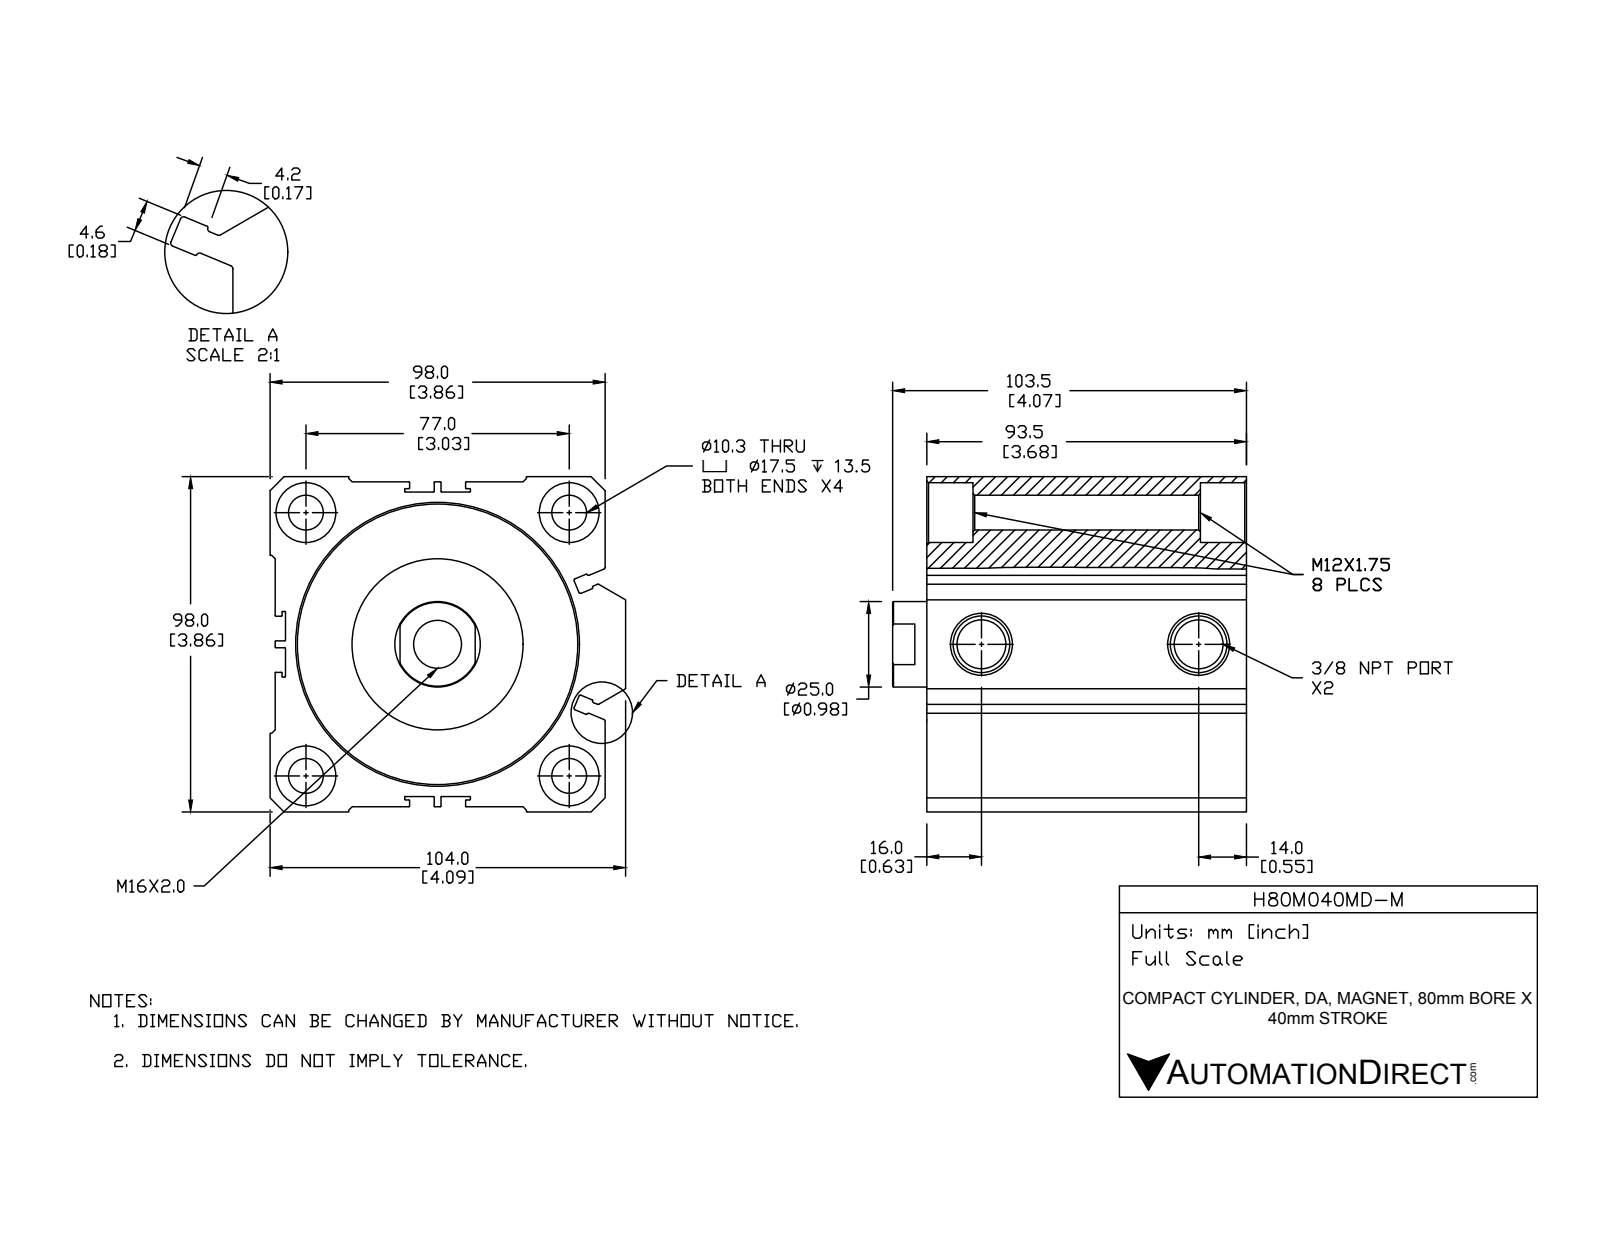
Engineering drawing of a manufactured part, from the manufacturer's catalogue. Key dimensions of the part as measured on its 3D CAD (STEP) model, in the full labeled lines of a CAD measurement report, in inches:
Part name (STEP PRODUCT): H80M040MD-M-BODY; H80M040MD-M; H80M040MD-M-PISTON
STEP written by: SolidWorks 2015 (CONFIG_CONTROL_DESIGN)
Units: inches
Bodies: 2 solids, 261 faces (105 planar, 103 cylindrical, 53 other)
Overall size (bounding box): 4.094 × 4.075 × 3.858
Volume: 36.88 in³ · Surface area: 203.9 in²
Round holes (diameter × count): ⌀0.402 ×4, ⌀0.689 ×4, ⌀0.562 ×2, ⌀0.551 ×1, ⌀0.984 ×1, ⌀1.792 ×1, ⌀3.15 ×1, ⌀3.228 ×1
Round bosses / shafts (diameter × count): ⌀1.969 ×1, ⌀1.535 ×1
Partial cylindrical surfaces — rounded edges, fillets, slot ends (radius × count): R0.008 ×40, R0.02 ×12
Main face-to-face distances: 0.059, 3.799, 3.681, 3.858, 1.969, 0.354, 0.177, 0.118, 1.421, 1.067
Hole centre spacings: 2.144, 3.031, 4.287, 2.5
